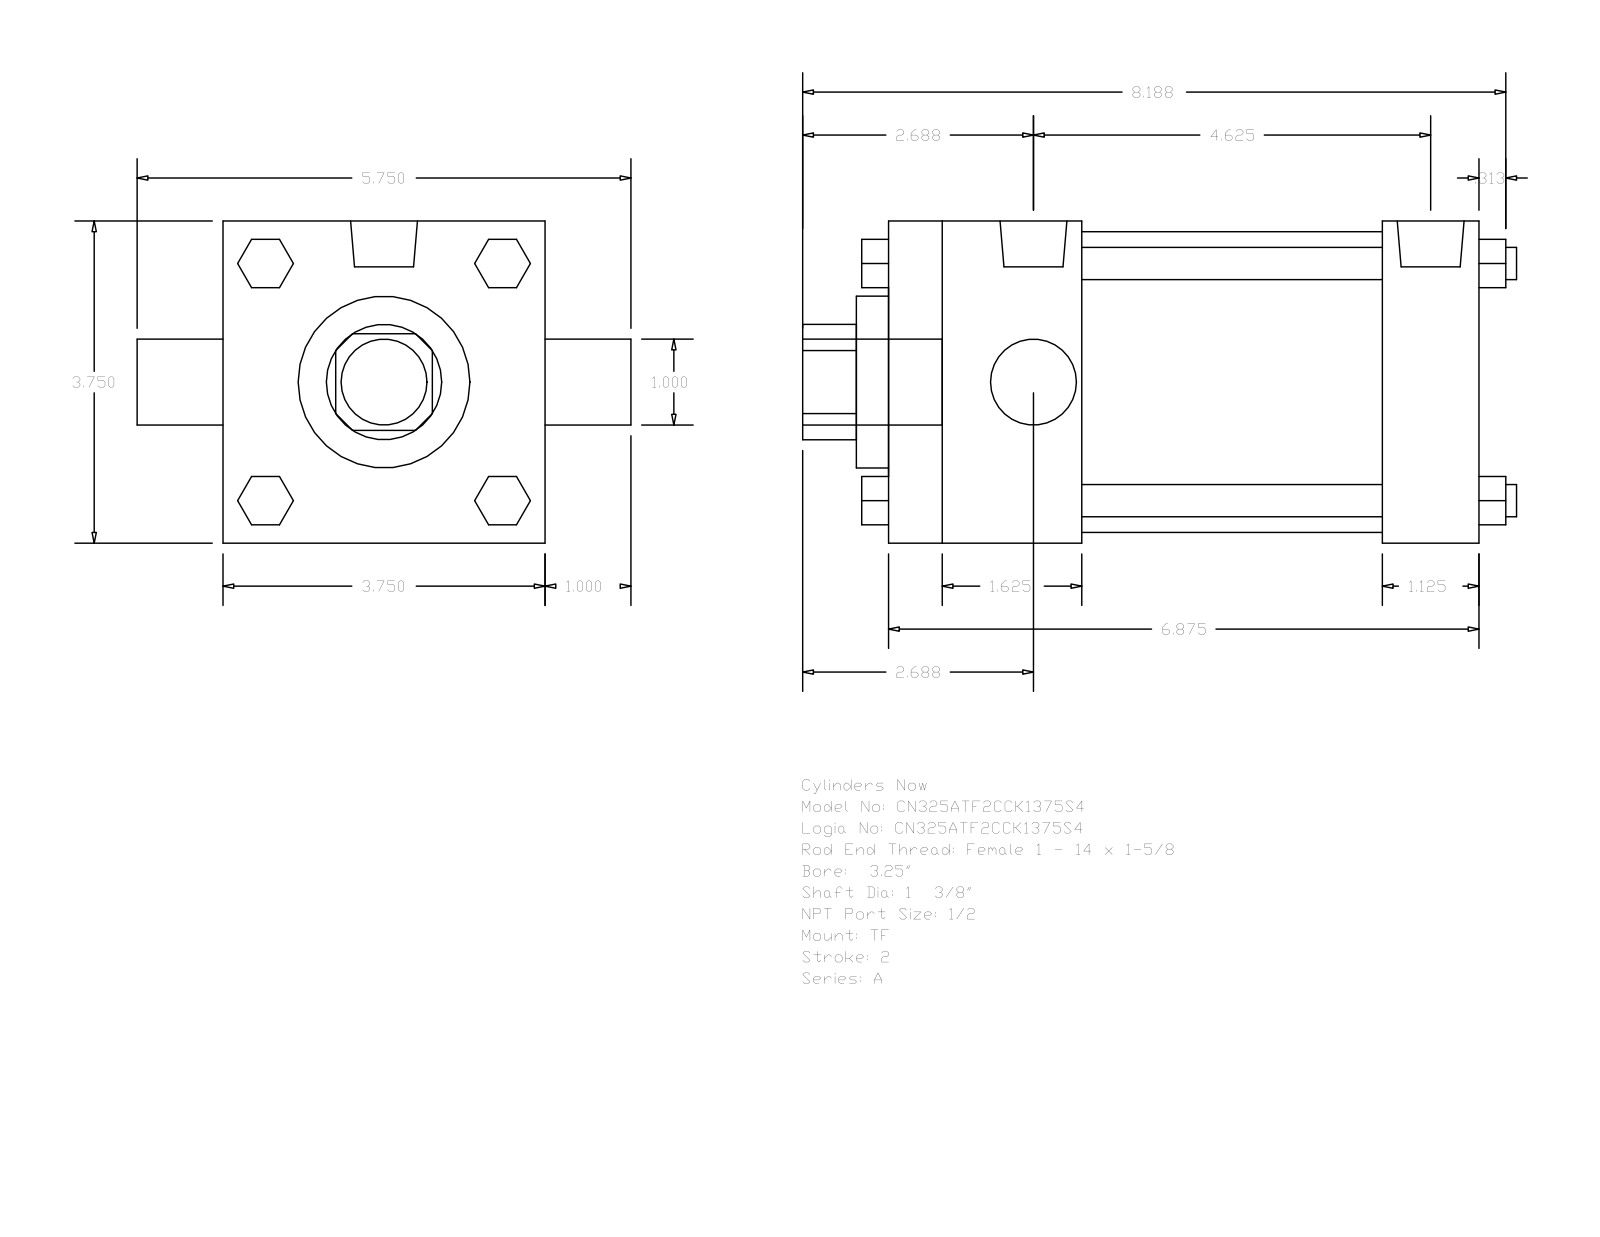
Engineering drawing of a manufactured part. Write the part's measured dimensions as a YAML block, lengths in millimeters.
part_name: "A_TF__0325_1.375"
step_written_by: "GSSL Pune (CONFIG_CONTROL_DESIGN)"
units: millimeters
bodies: {solids: 0, faces: 120, planar: 92, cylindrical: 28, other: 0}
overall_size: [211.14, 146.05, 95.25]
round_holes:
  - {diameter: 25.4, count: 1}
  - {diameter: 34.92, count: 1}
  - {diameter: 50.8, count: 1}
  - {diameter: 88.9, count: 1}
round_bosses_or_shafts:
  - {diameter: 9.53, count: 4}
  - {diameter: 8.73, count: 3}
  - {diameter: 19.77, count: 2}
  - {diameter: 25.4, count: 1}
partial_cylinders:
  - {radius: 17.06, count: 1}
face_to_face_distances: [95.24, 174.63, 28.58, 57.15, 146.05, 88.9, 117.48, 9.52, 66.67, 155.57]
